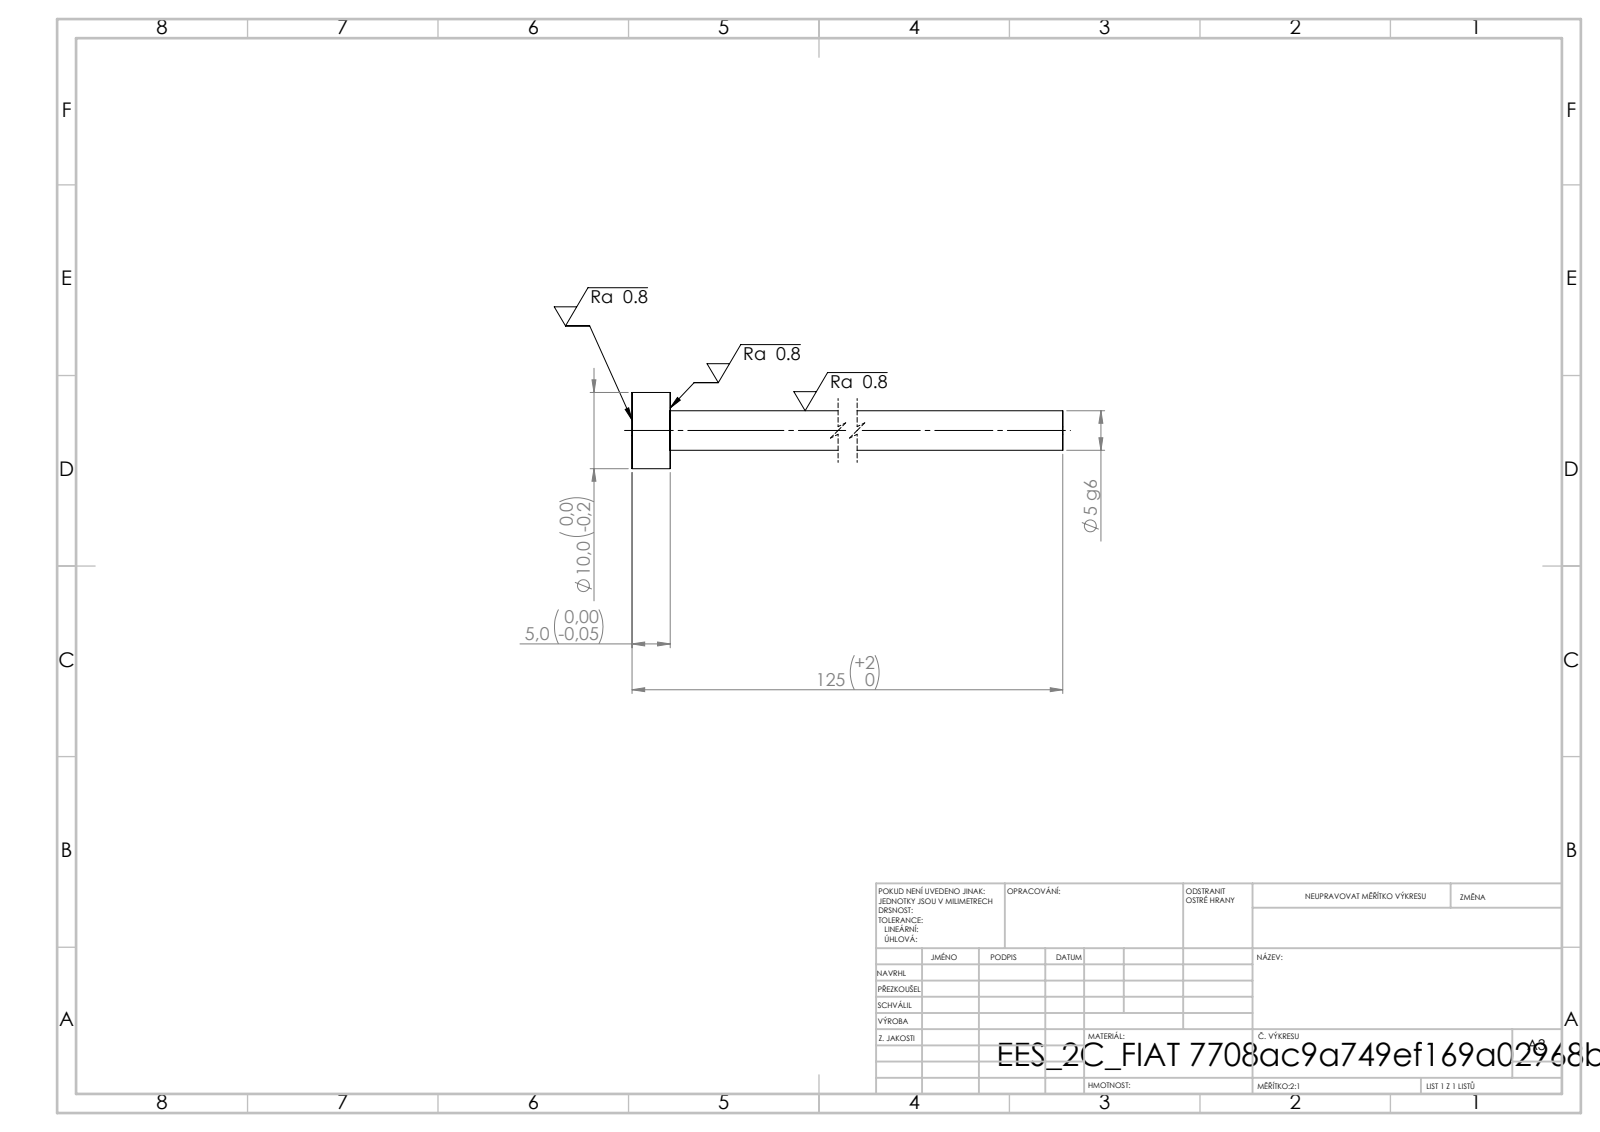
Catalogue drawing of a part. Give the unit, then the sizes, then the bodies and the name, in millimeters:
Units: millimetres
Overall size (bounding box): 125 × 10 × 10
Round bosses / shafts (diameter × count): ⌀10 ×1, ⌀5.2 ×1
Main face-to-face distances: 5, 125, 120
Volume: 2 941 mm³ · Surface area: 2 275 mm²
Bodies: 1 solid, 7 faces (3 planar, 4 cylindrical, 0 other)
STEP written by: SolidWorks 2019 (CONFIG_CONTROL_DESIGN)
